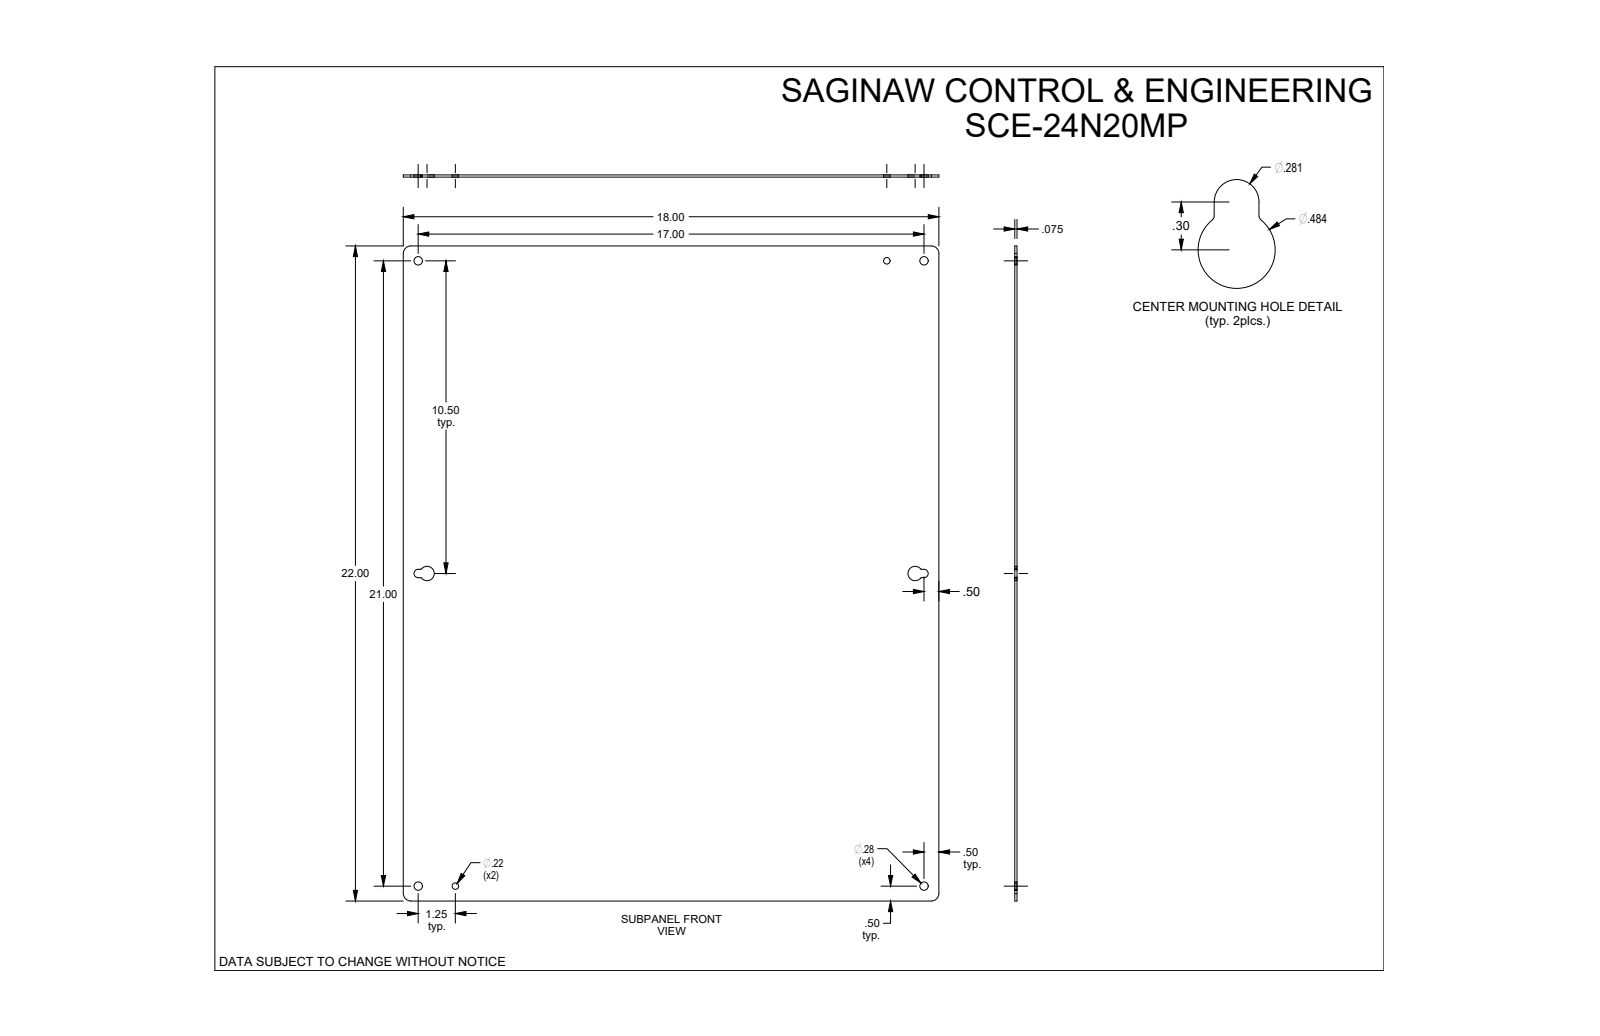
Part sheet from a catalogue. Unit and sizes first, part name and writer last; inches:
Units: inches
Overall size (bounding box): 22 × 18 × 0.075
Round holes (diameter × count): ⌀0.281 ×4, ⌀0.218 ×2
Partial cylindrical surfaces — rounded edges, fillets, slot ends (radius × count): R0.03 ×4, R0.25 ×4, R0.141 ×2, R0.242 ×2
Main face-to-face distances: 0.075, 18, 22, 10.859, 11.141, 0.281
Hole centre spacings: 1.25, 15.75, 17, 21, 21.037, 26.25, 27.019, 25.52
Volume: 29.64 in³ · Surface area: 796.9 in²
Bodies: 1 solid, 28 faces (10 planar, 18 cylindrical, 0 other)
Part name (STEP PRODUCT): SCE-24N20MP
STEP written by: SolidWorks 2019 (CONFIG_CONTROL_DESIGN)
